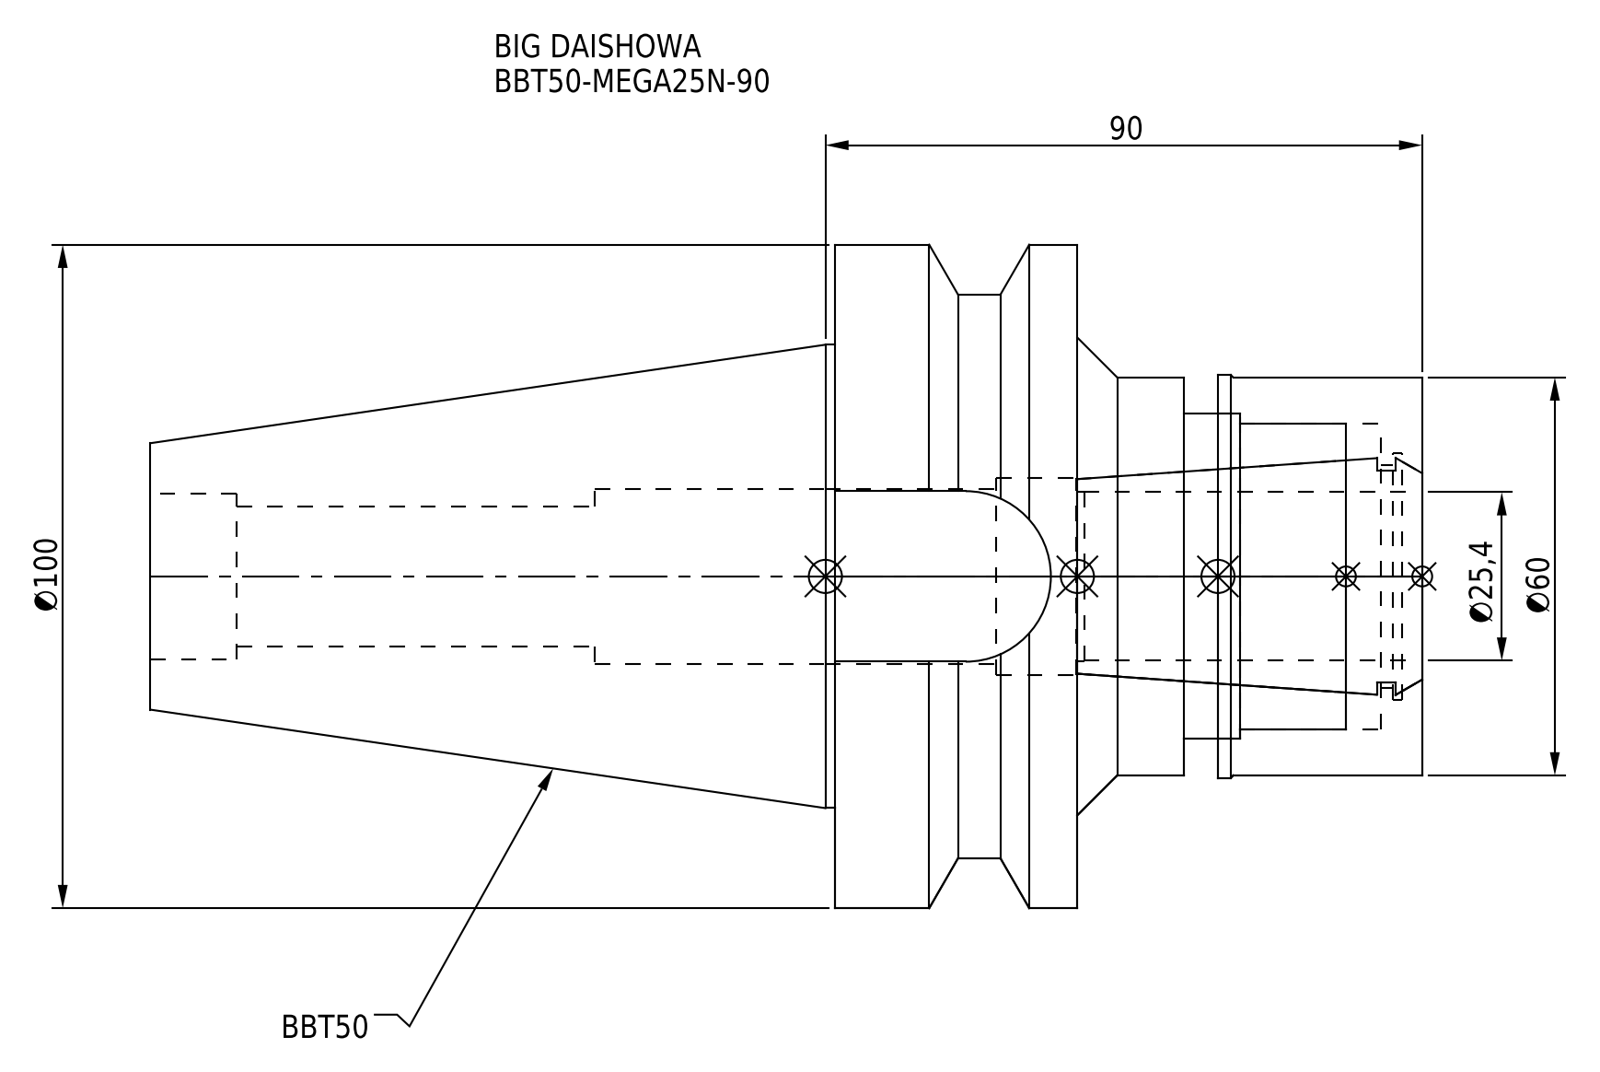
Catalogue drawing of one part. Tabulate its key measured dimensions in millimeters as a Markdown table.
| quantity | value |
| --- | --- |
| part name | BBT50-MEGA25N-90-254-FreeParts; DXF_TEMP_ASSY_ASM_4_ASM.stp; BBT50-MEGA25N-90_1.stp; BBT50-MEGA25N-90 (+3 more) |
| STEP written by | SolidWorks 2019 (CONFIG_CONTROL_DESIGN) |
| units | millimeters |
| bodies | 2 solids, 74 faces (22 planar, 38 cylindrical, 14 other) |
| overall size | 191.8 × 100 × 100 |
| volume | 530 751 mm³ |
| surface area | 79 843 mm² |
| round holes (diameter × count) | 21.2 × 1, 25 × 1, 26.3 × 1, 29.6 × 1, 33.5 × 1, 37.2 × 1, 46 × 1, 49 × 1 |
| round bosses / shafts (diameter × count) | 100 × 1, 85 × 1, 69.85 × 1, 60.7 × 1, 60 × 1 |
| partial cylindrical surfaces (radius × count) | 12.85 × 1 |
| main face-to-face distances | 36.5, 52, 88.5, 30.8, 21.2, 57.7, 35.9, 5.1, 16.1, 52.6 |
